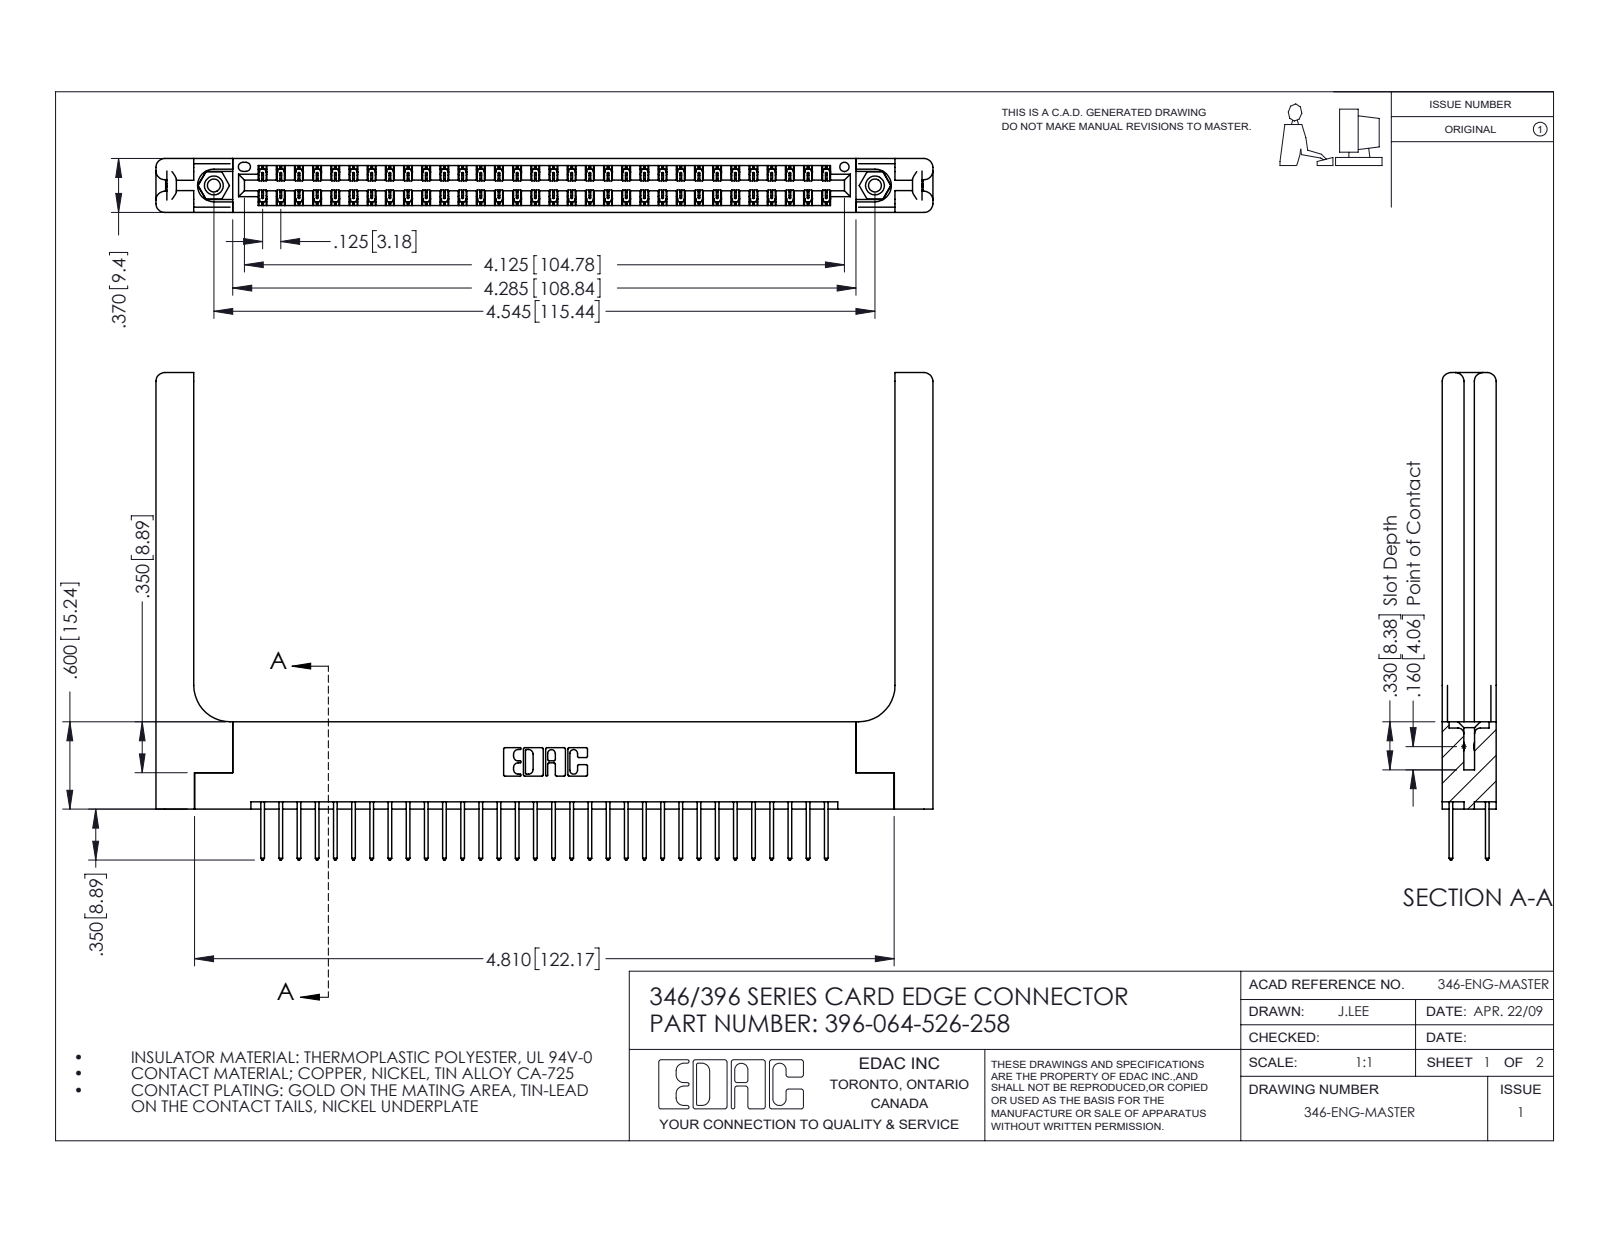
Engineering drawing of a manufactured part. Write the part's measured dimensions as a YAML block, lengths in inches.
part_name: "345-292-001_345-293-126; 346-220-058_345-220-058; 396-064-526-258; 346 Part_Flush Mounting Lugs - 0.156 Dia-TH (+1 more)"
step_written_by: "SolidWorks 2016 (CONFIG_CONTROL_DESIGN)"
units: inches
bodies: {solids: 69, faces: 3706, planar: 2464, cylindrical: 1182, other: 60}
overall_size: [5.341, 3.35, 0.37]
volume: 1.266
surface_area: 36.44
round_holes:
  - {diameter: 0.089, count: 2}
  - {diameter: 0.125, count: 2}
  - {diameter: 0.156, count: 2}
  - {diameter: 0.064, count: 1}
round_bosses_or_shafts:
  - {diameter: 0.155, count: 2}
partial_cylinders:
  - {radius: 0.006, count: 96}
  - {radius: 0.01, count: 64}
  - {radius: 0.01, count: 22}
  - {radius: 0.06, count: 16}
  - {radius: 0.007, count: 6}
  - {radius: 0.031, count: 6}
  - {radius: 0.026, count: 3}
  - {radius: 0.014, count: 2}
face_to_face_distances: [0.37, 0.048, 0.322, 0.072, 0.25, 0.148, 0.15, 0.025, 0.298, 0.275]
hole_center_spacings: [0.246, 4.337, 4.545]
